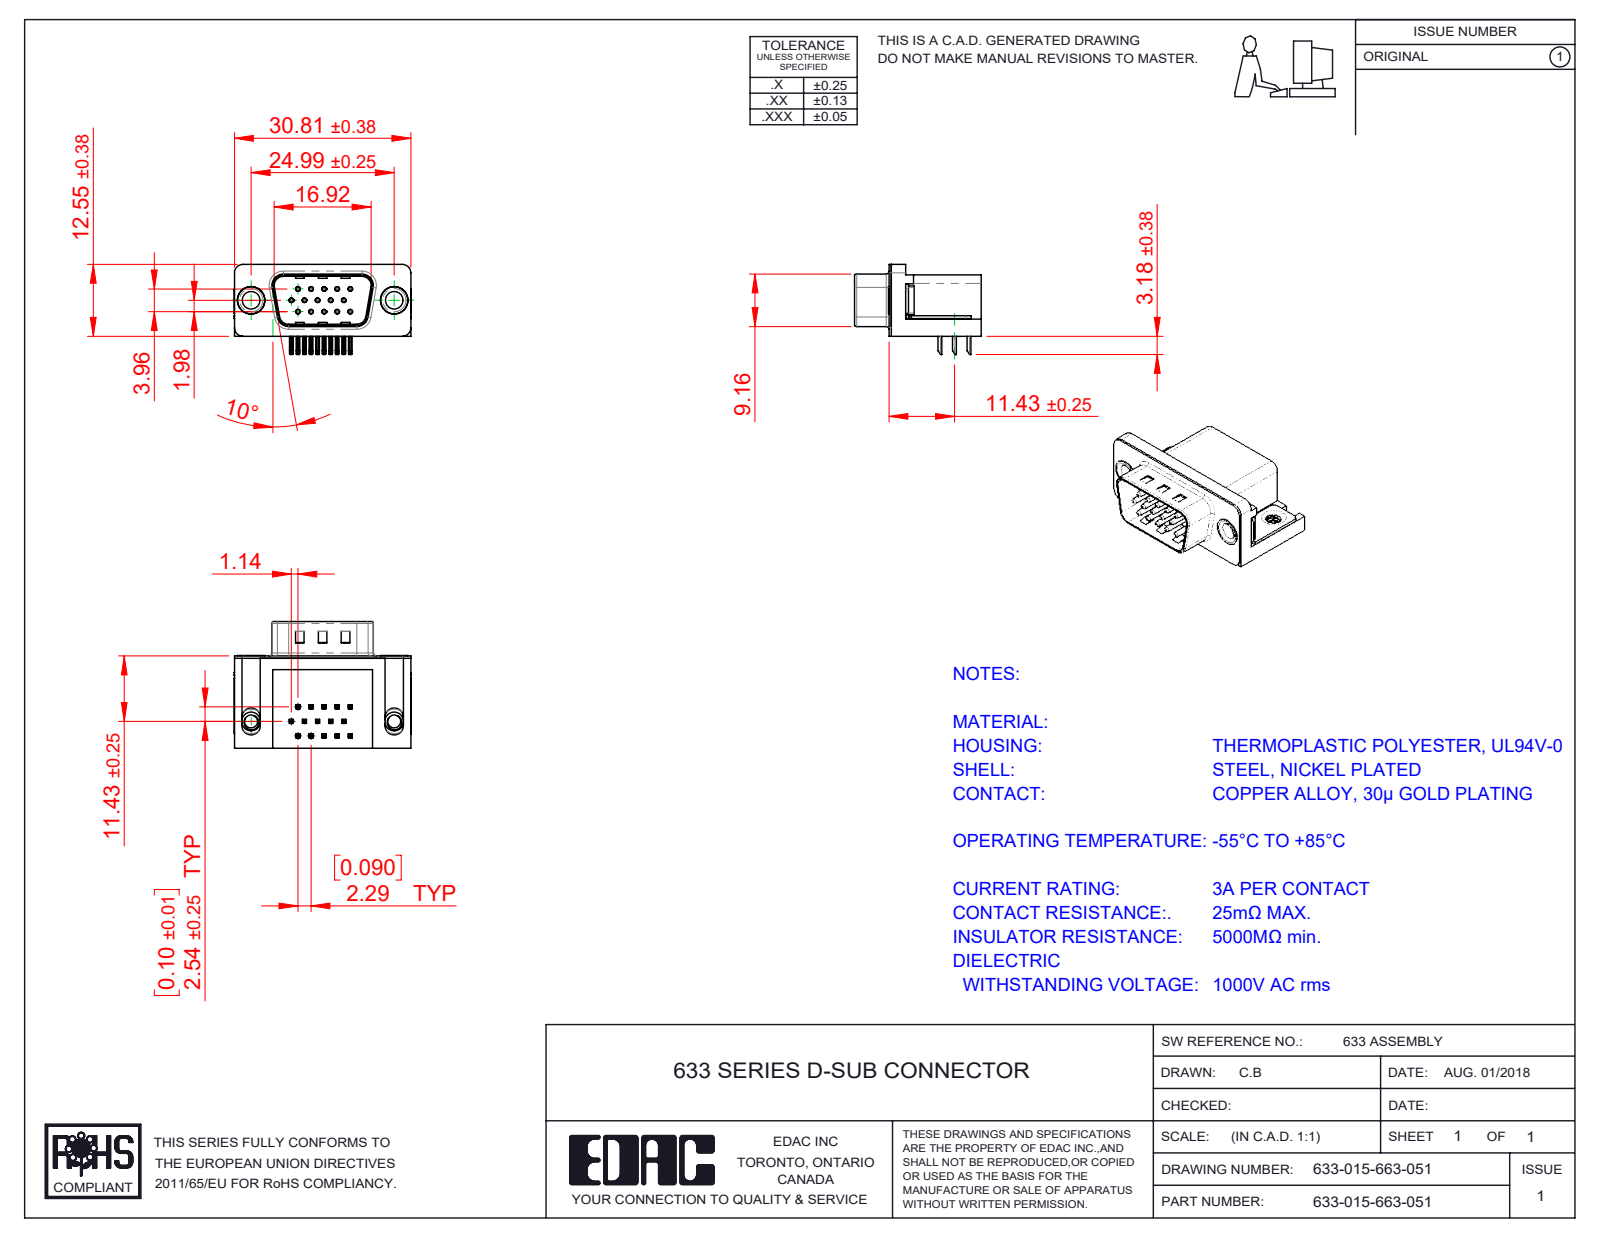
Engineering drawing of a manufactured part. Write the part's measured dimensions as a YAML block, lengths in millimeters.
part_name: "633 Housing_15 Contact; 633 Contact Top; 633 Shell_15 Contact; 633-015-663-051 (+4 more)"
step_written_by: "SolidWorks 2016 (CONFIG_CONTROL_DESIGN)"
units: millimeters
bodies: {solids: 21, faces: 1433, planar: 861, cylindrical: 437, other: 135}
overall_size: [30.89, 22.1, 15.73]
volume: 4074
surface_area: 5486
round_holes:
  - {diameter: 0.35, count: 15}
  - {diameter: 0.8, count: 15}
  - {diameter: 2.26, count: 2}
  - {diameter: 3.05, count: 2}
  - {diameter: 4, count: 2}
  - {diameter: 4.8, count: 2}
  - {diameter: 5, count: 2}
round_bosses_or_shafts:
  - {diameter: 0.75, count: 15}
  - {diameter: 4.9, count: 2}
  - {diameter: 4.75, count: 2}
  - {diameter: 3.85, count: 2}
  - {diameter: 3.26, count: 2}
partial_cylinders:
  - {radius: 0.25, count: 68}
  - {radius: 0.12, count: 30}
  - {radius: 1, count: 16}
  - {radius: 0.5, count: 9}
  - {radius: 1.6, count: 8}
  - {radius: 1.5, count: 7}
  - {radius: 0.9, count: 4}
  - {radius: 2, count: 4}
face_to_face_distances: [0.4, 10.35, 15.7, 0.5, 2.9, 2.5, 6.7, 16.1, 0.35, 10.7]
hole_center_spacings: [3.96, 2.28, 4.57, 2.29, 6.05, 6.86, 7.92, 6.04]
